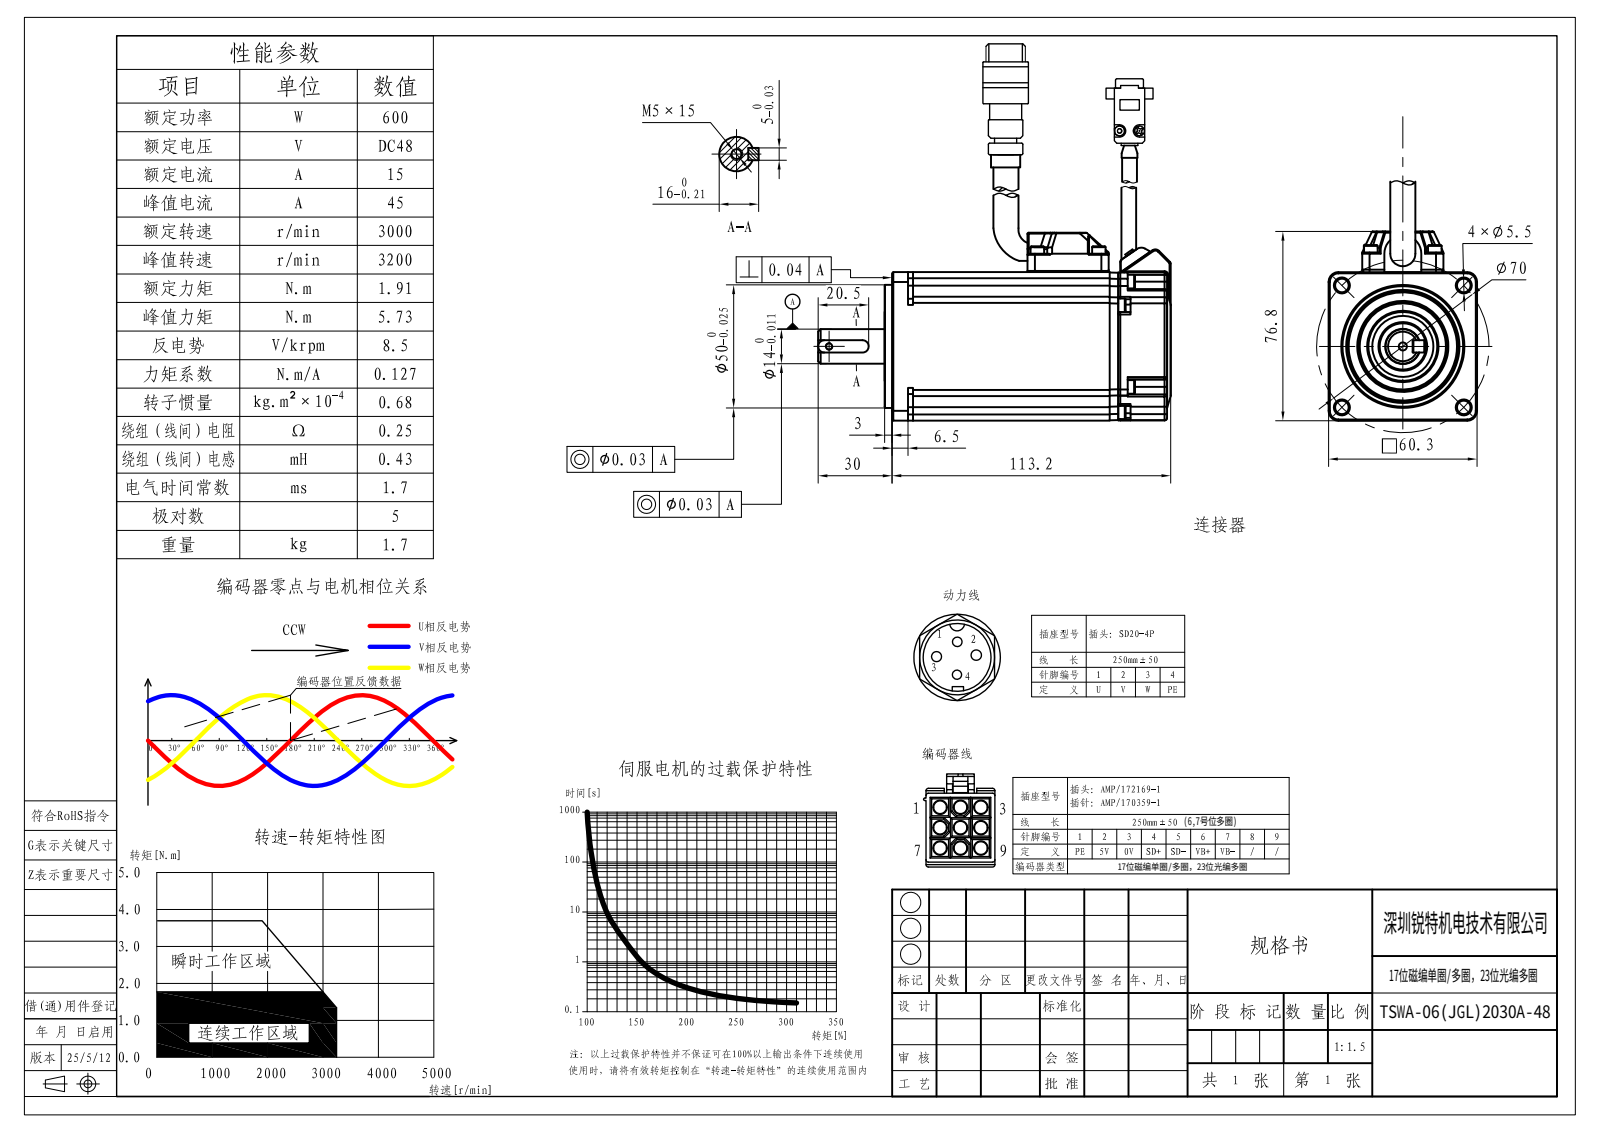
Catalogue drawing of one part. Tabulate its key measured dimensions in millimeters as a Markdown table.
| quantity | value |
| --- | --- |
| part name | WB60ST-M01930 |
| STEP written by | SolidWorks 2018 (CONFIG_CONTROL_DESIGN) |
| units | millimeters |
| bodies | 27 solids, 1213 faces (466 planar, 480 cylindrical, 267 other) |
| overall size | 143.2 × 73.3 × 60.3 |
| volume | 136 440 mm³ |
| surface area | 92 380 mm² |
| round holes (diameter × count) | 2 × 15, 2.5 × 15, 3.5 × 8, 2.05 × 4, 3.4 × 4, 5.5 × 4, 2.8 × 2, 3.3 × 2, 4.2 × 1, 5 × 1, 5.8 × 1, 6 × 1 |
| round bosses / shafts (diameter × count) | 5.5 × 10, 3 × 10, 5 × 4, 4 × 2, 2.2 × 2, 52.6 × 1, 38 × 1, 36 × 1 |
| partial cylindrical surfaces (radius × count) | 1 × 40, 2.5 × 26, 0.5 × 24, 2 × 16, 3 × 13, 0.6 × 9, 4.5 × 8, 4 × 4 |
| main face-to-face distances | 60.3, 1.5, 10, 50.3, 19.8, 50.15, 4.3, 113.2, 60.15, 1 |
| hole center spacings | 8, 8.29, 31.5, 41.49, 44.54, 52.09, 66.07, 19.49 |
